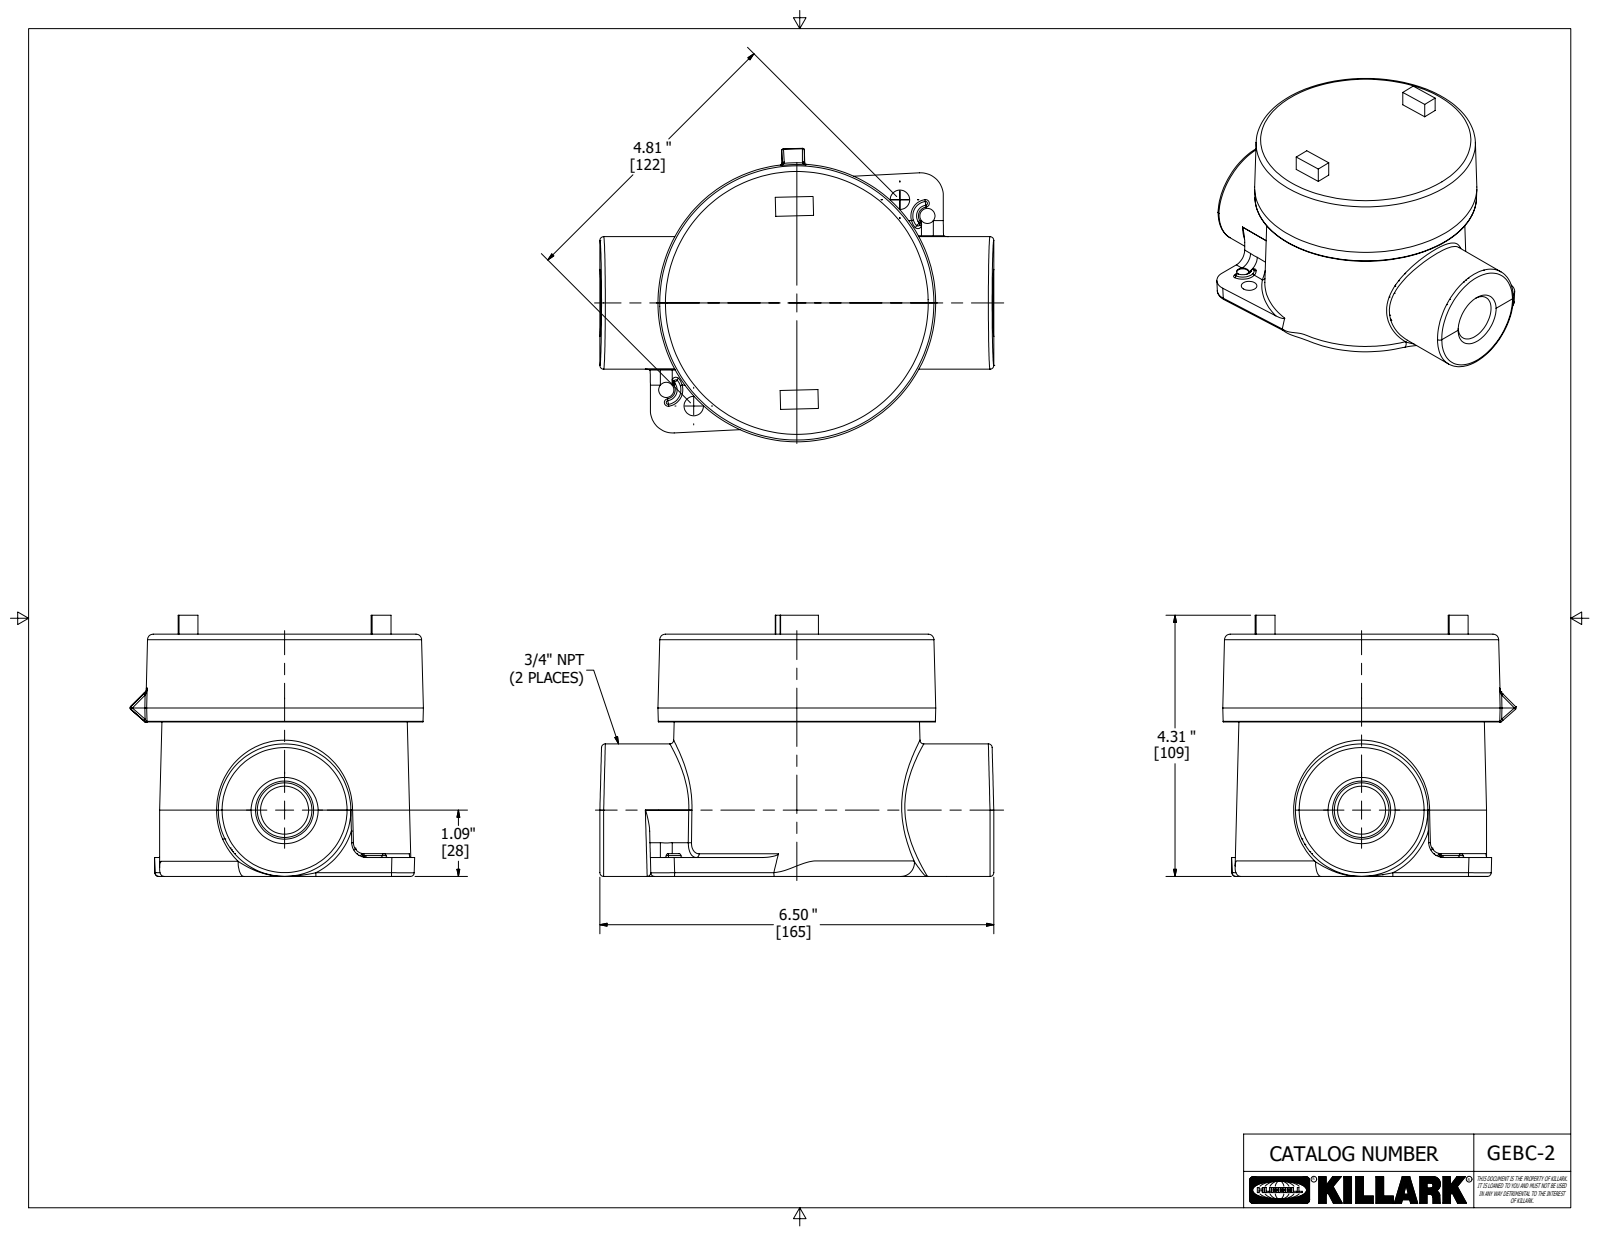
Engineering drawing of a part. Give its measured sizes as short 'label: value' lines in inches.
name: GEBC-2; 21389; 21147-override
written by: Autodesk Inventor 2020 (AUTOMOTIVE_DESIGN)
unit: in
bodies: 2 solids, 265 faces (57 planar, 70 cylindrical, 138 other)
size: 6.502 × 4.843 × 4.31
volume: 37.79 in³; area: 200.9 in²
holes: 2× ⌀0.25, 2× ⌀0.321, 1× ⌀0.165, 1× ⌀0.792, 1× ⌀0.959, 1× ⌀3.823, 1× ⌀4.045
bosses: 1× ⌀4, 1× ⌀3.845, 1× ⌀2.187
rounds: 17× R0.062, 6× R0.25, 3× R0.031, 2× R0.03, 2× R0.375, 2× R0.779, 1× R0.625, 1× R2.063
face distances: 3.998, 3.56, 0.438, 2.549, 1.011, 1.449, 0.155, 3.03, 0.375, 2.174
hole spacings: 2.589, 4.972, 0.526, 0.526, 1.301, 2.191, 2.291, 2.406
